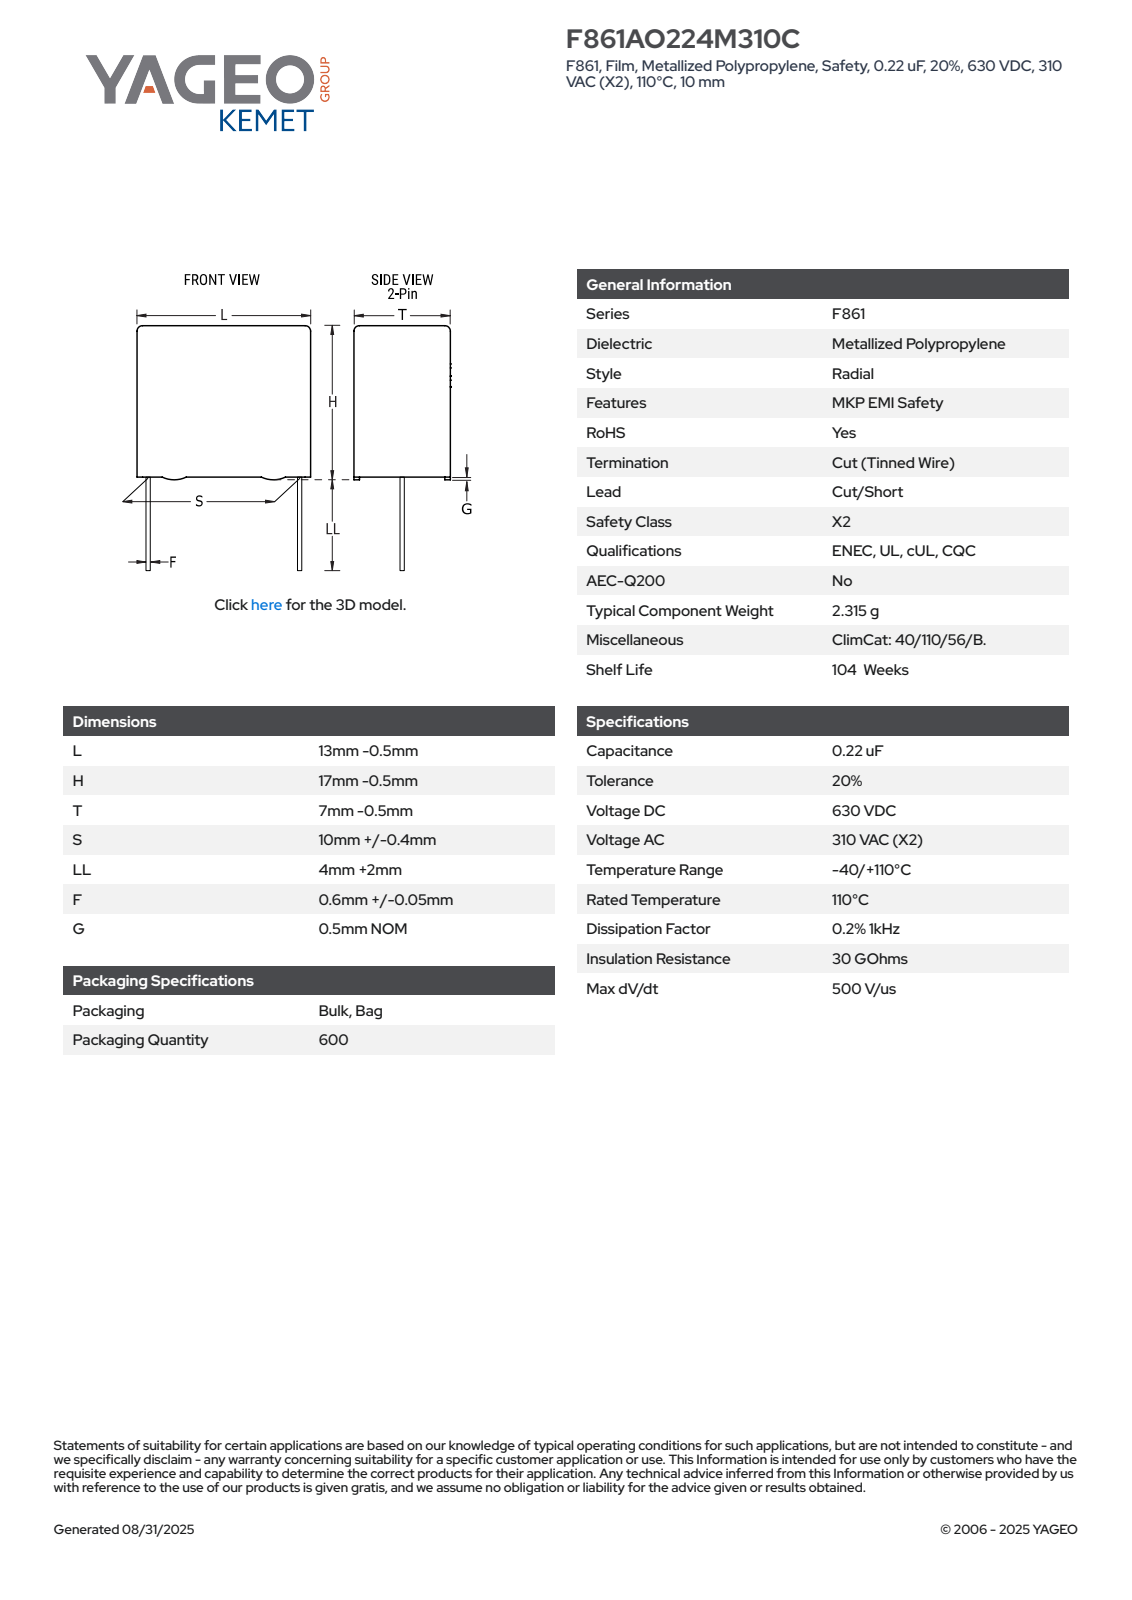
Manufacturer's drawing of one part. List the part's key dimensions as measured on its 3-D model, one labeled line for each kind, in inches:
Part name (STEP PRODUCT): CFR_RBG_13X17X7_L12.5H16.5T6.5S10LL6F0.65G0.5
STEP written by: SolidWorks 2014 (AUTOMOTIVE_DESIGN)
Units: inches
Bodies: 4 solids, 89 faces (81 planar, 8 cylindrical, 0 other)
Overall size (bounding box): 0.886 × 0.492 × 0.256
Volume: 0.08 in³ · Surface area: 1.26 in²
Round bosses / shafts (diameter × count): ⌀0.026 ×2
Partial cylindrical surfaces — rounded edges, fillets, slot ends (radius × count): R0.02 ×4
Main face-to-face distances: 0.256, 0.492, 0.63, 0.015, 0.241, 0.02, 0.65, 0.227, 0.236, 0.886
